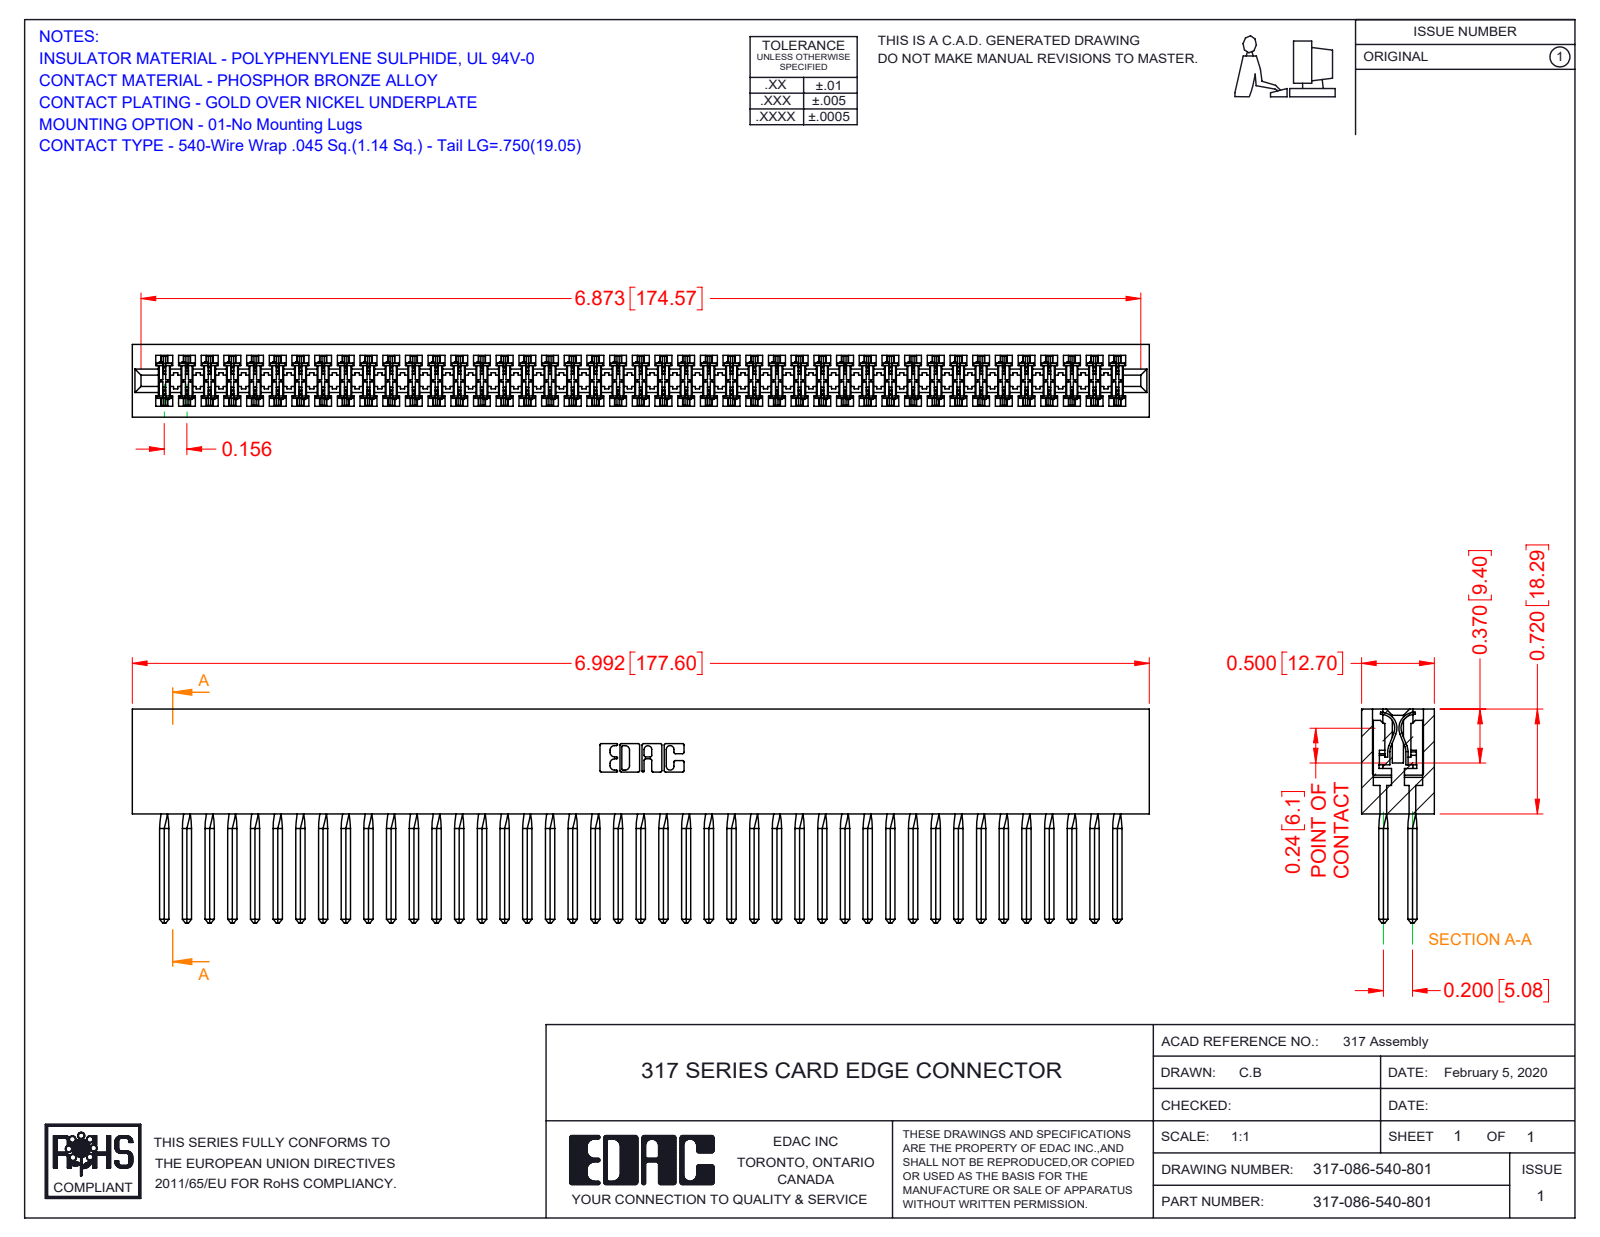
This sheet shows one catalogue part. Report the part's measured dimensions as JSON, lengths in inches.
{"part_name": "317-086-540-801; 317-290-001_540; 317 Part_Lugless", "step_written_by": "SolidWorks 2016 (CONFIG_CONTROL_DESIGN)", "units": "inches", "bodies": {"solids": 87, "faces": 7744, "planar": 6328, "cylindrical": 1072, "other": 344}, "overall_size": [6.992, 1.47, 0.5], "volume_in3": 1.93, "surface_area_in2": 73.56, "partial_cylinders_radius": [[0.015, 172], [0.01, 22], [0.007, 6], [0.031, 6], [0.026, 3], [0.095, 2], [0.1, 2], [0.11, 2]], "face_to_face_distances": [0.075, 0.5, 0.425, 0.35, 0.195, 0.094, 0.2, 0.115, 0.131, 0.046]}
